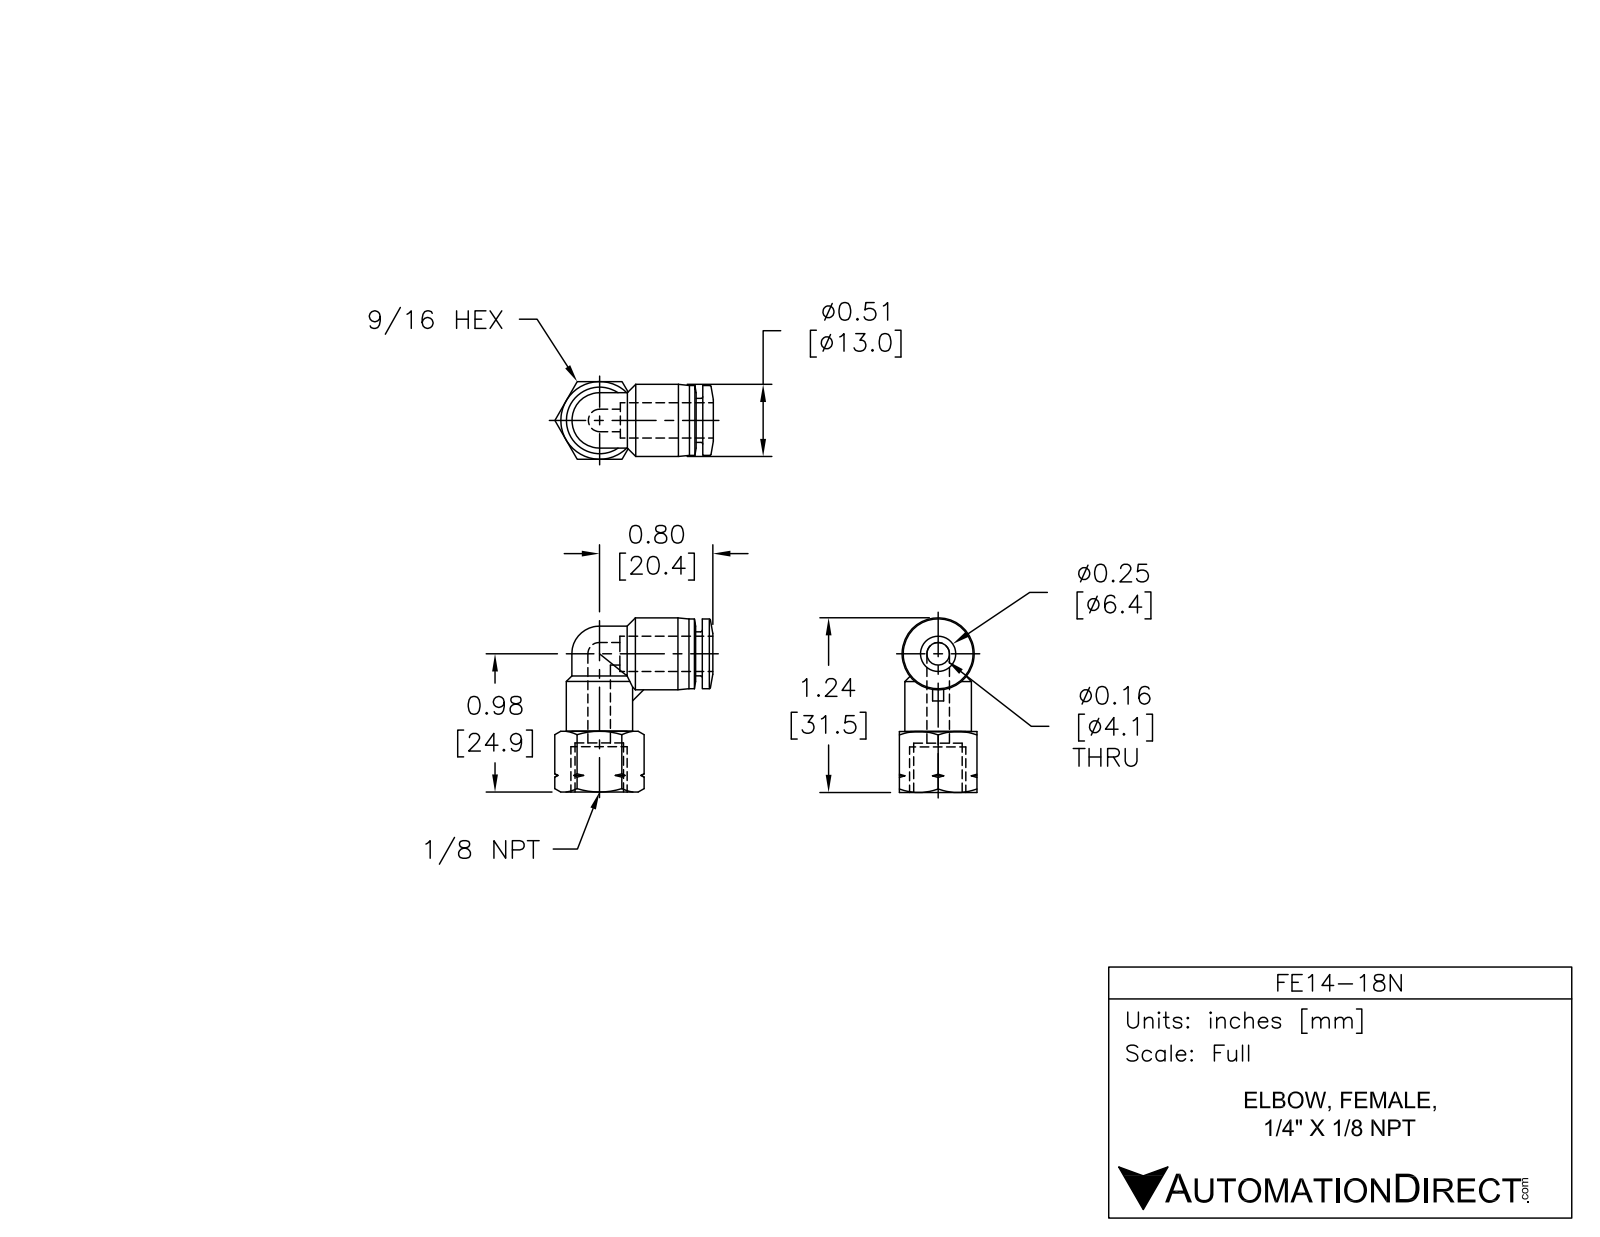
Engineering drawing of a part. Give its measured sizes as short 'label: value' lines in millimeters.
name: FE14-18N
written by: SolidWorks 2015 (AUTOMOTIVE_DESIGN)
unit: mm
bodies: 1 solid, 86 faces (15 planar, 20 cylindrical, 51 other)
size: 31.5 × 28.6 × 14
volume: 3 980 mm³; area: 3 087 mm²
holes: 2× ⌀4, 1× ⌀6.6
bosses: 2× ⌀10, 1× ⌀13, 1× ⌀12.6, 1× ⌀12, 1× ⌀8
face distances: 14, 9, 2, 11, 1.2, 13.7, 14.9, 6, 8
